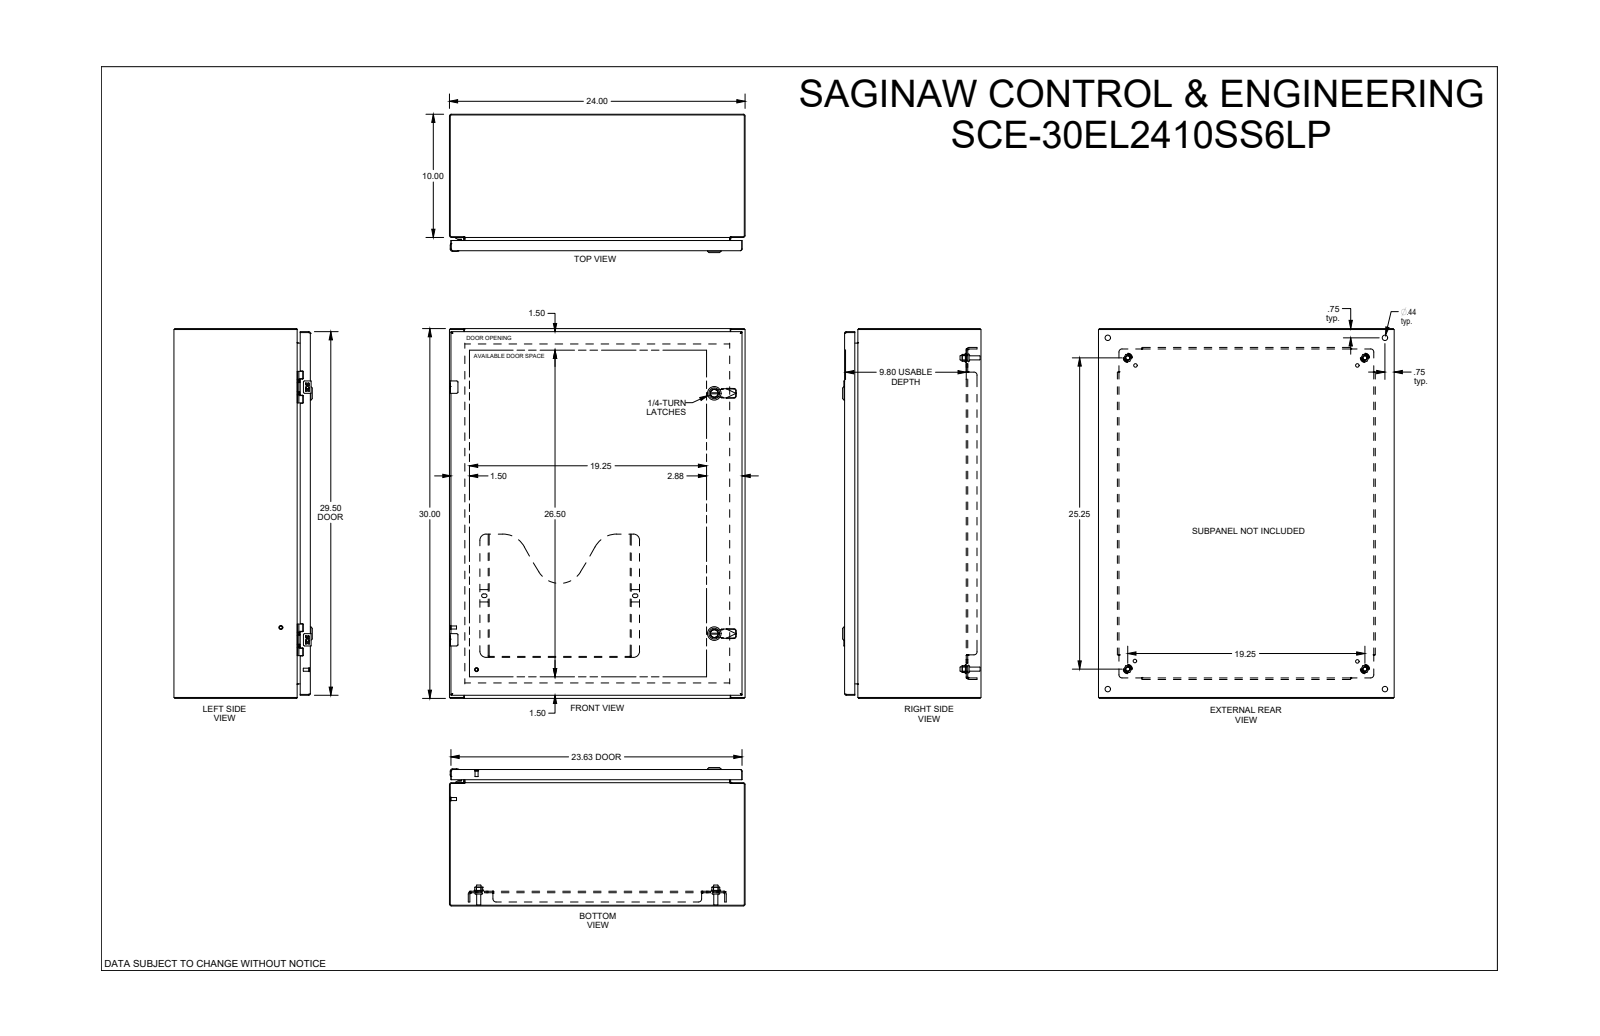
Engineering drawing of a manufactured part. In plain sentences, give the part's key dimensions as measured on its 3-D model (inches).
The part is named "SCE-30EL2410LP". Its 3-D file was written by "SolidWorks 2021 (AUTOMOTIVE_DESIGN)". It is 47 solids with 2843 faces: 1115 planar, 858 cylindrical and 870 other. Overall it measures 30 by 24 by 11.23 inches. Its volume is 303.3 cubic inches and its surface area 7 320 square inches. Round holes: 4 of diameter 0.172, 4 of diameter 0.205, 4 of diameter 0.244, 4 of diameter 0.266, 4 of diameter 0.281, 4 of diameter 0.367, 4 of diameter 0.375, 4 of diameter 0.437, 4 of diameter 0.5, 2 of diameter 0.04, 2 of diameter 0.188, 2 of diameter 0.197. Round bosses or shafts: 6 of diameter 0.17, 4 of diameter 0.366, 4 of diameter 0.332, 4 of diameter 0.25, 4 of diameter 0.248, 4 of diameter 0.24, 3 of diameter 0.196, 2 of diameter 1.102. Partial cylindrical surfaces (rounded edges, fillets, slot ends): 56 of radius 0.012, 28 of radius 0.01, 24 of radius 0.015, 20 of radius 0.02, 17 of radius 0.04, 13 of radius 0.06, 12 of radius 0.029, 12 of radius 0.1. The main face-to-face distances are 0.075, 0.06, 11.073, 10.998, 11.013, 10.938, 1.2, 9.873, 23.925, 1. The hole center spacings are 0.985, 20.5, 0.02, 0.493, 0.494, 0.875, 2.298, 4.493.
